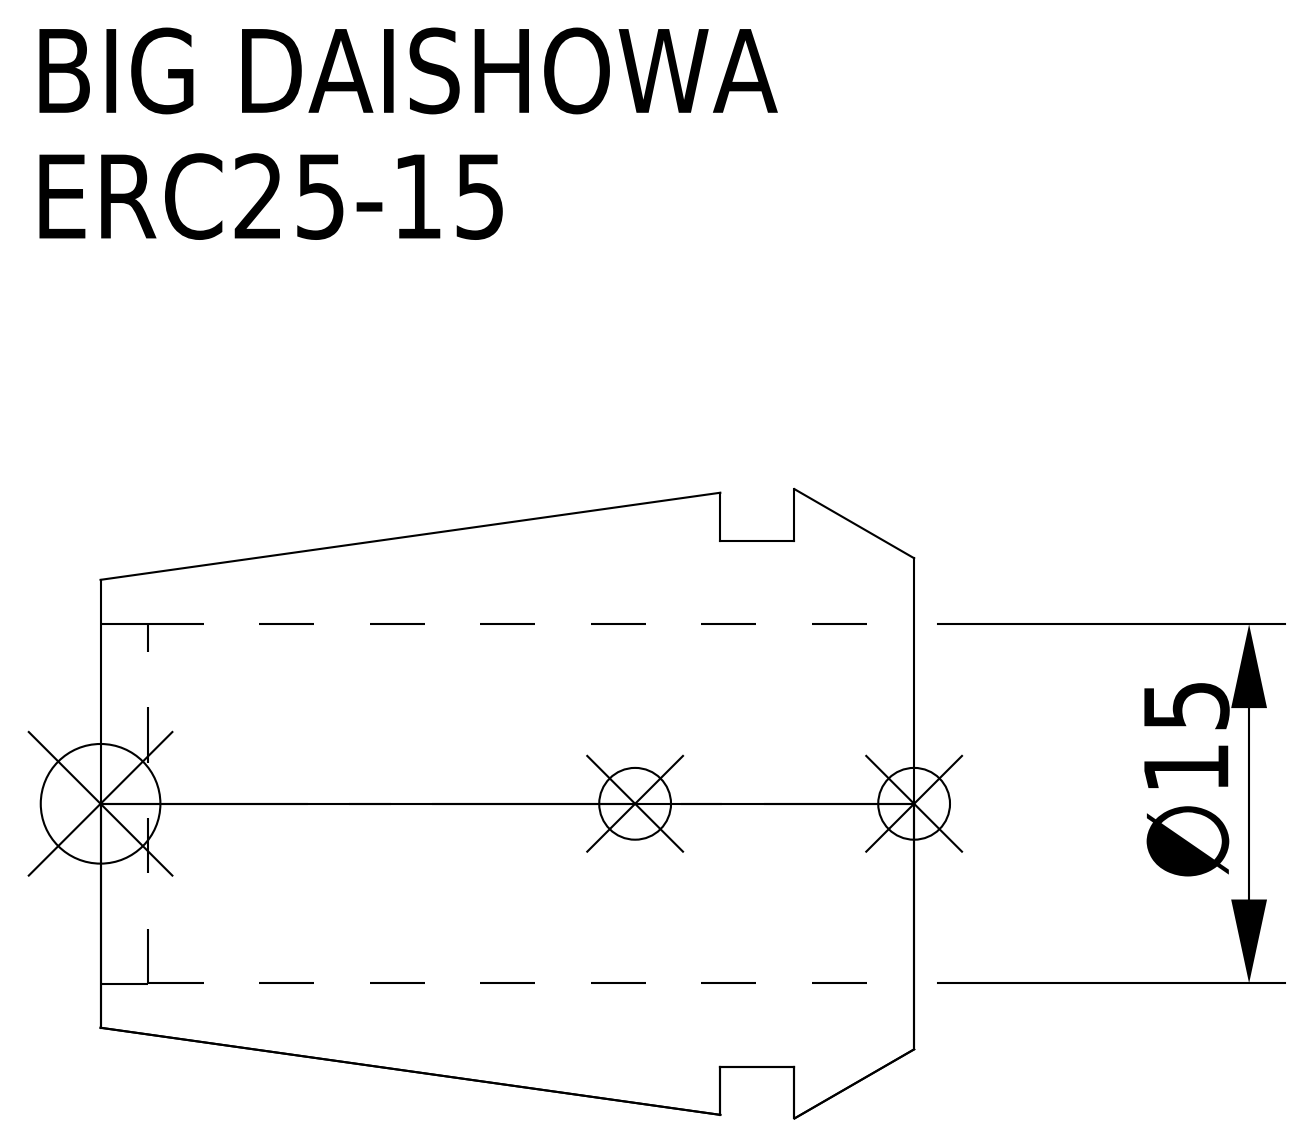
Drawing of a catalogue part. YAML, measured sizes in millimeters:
part_name: "ERC25-15"
step_written_by: "CREO PARAMETRIC BY PTC INC, 2016380 (AUTOMOTIVE_DESIGN)"
units: millimeters
bodies: {solids: 1, faces: 15, planar: 5, cylindrical: 6, other: 4}
overall_size: [34, 26.3, 26.3]
volume: 7592
surface_area: 4645
round_holes:
  - {diameter: 15, count: 1}
  - {diameter: 15.05, count: 1}
round_bosses_or_shafts:
  - {diameter: 22, count: 1}
face_to_face_distances: [5, 8.1, 3.1, 34, 29, 25.9, 32, 27, 23.9, 2]
